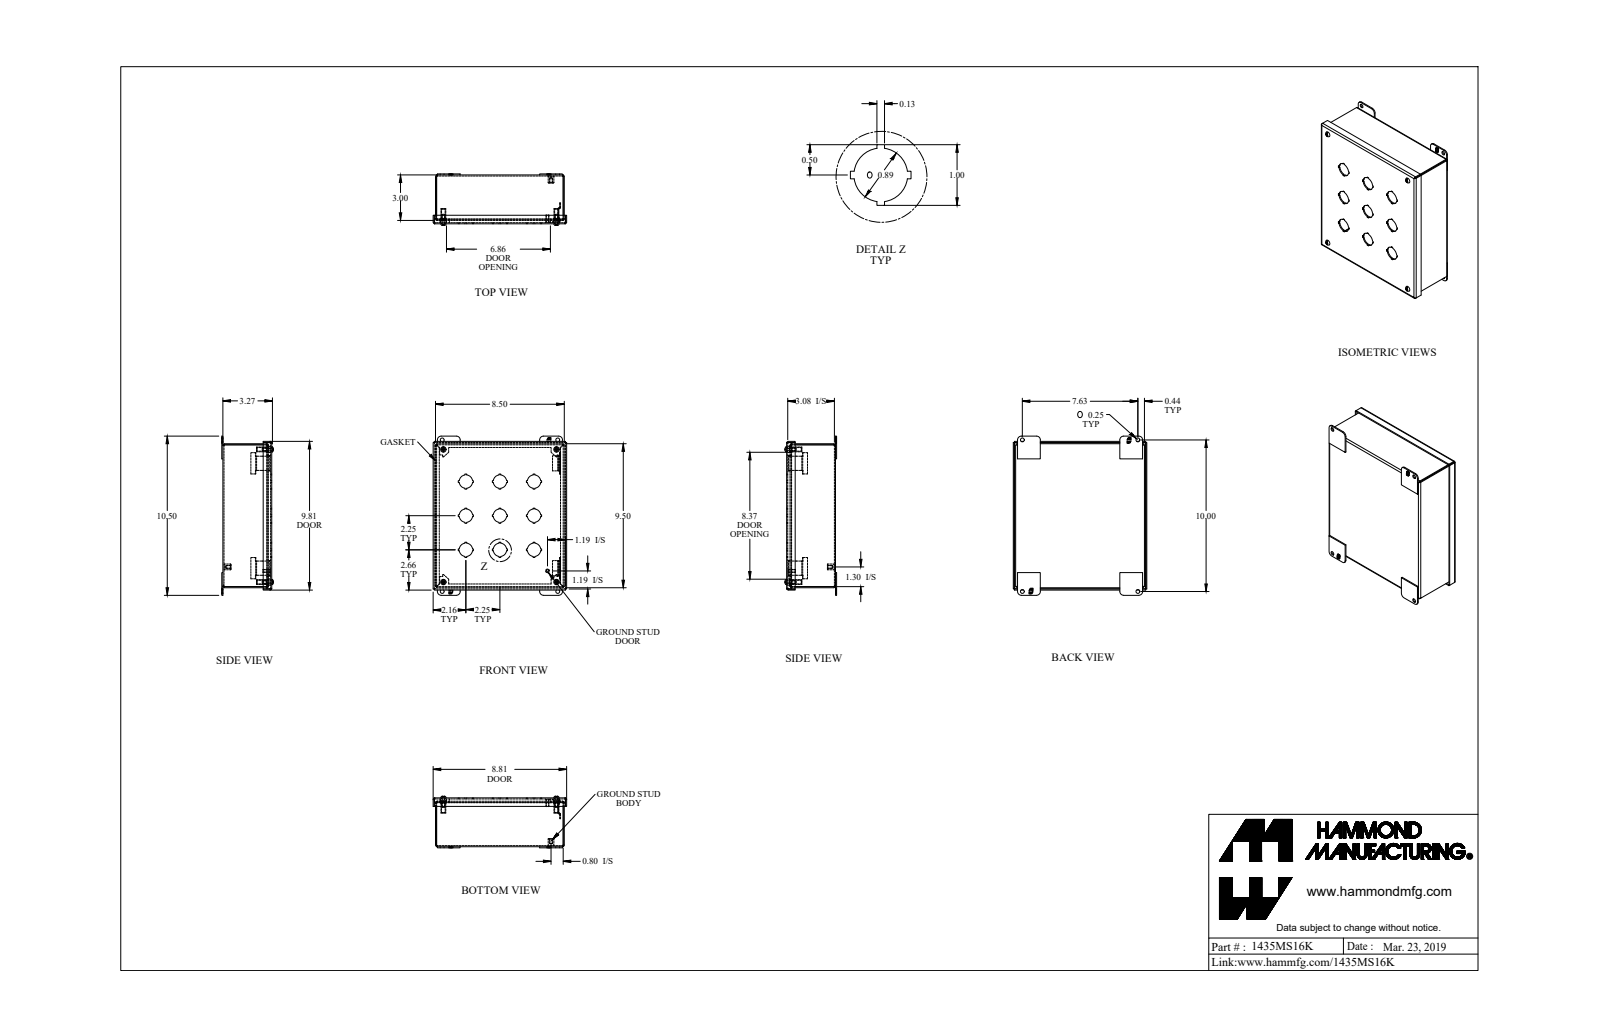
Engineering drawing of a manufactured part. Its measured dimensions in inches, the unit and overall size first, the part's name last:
Units: inches
Overall size (bounding box): 10.5 × 8.81 × 3.404
Round holes (diameter × count): ⌀0.886 ×9, ⌀0.25 ×8, ⌀0.065 ×4, ⌀0.239 ×4, ⌀0.253 ×4, ⌀0.406 ×4, ⌀0.156 ×1
Round bosses / shafts (diameter × count): ⌀0.19 ×5, ⌀0.406 ×4, ⌀0.315 ×4, ⌀0.148 ×4, ⌀0.375 ×1, ⌀0.25 ×1
Partial cylindrical surfaces — rounded edges, fillets, slot ends (radius × count): R0.036 ×12, R0.108 ×12, R0.25 ×8, R0.029 ×4, R0.086 ×4, R0.171 ×4
Main face-to-face distances: 0.072, 3.15, 3.222, 3.078, 8.428, 9.428, 0.155, 8.5, 8.356, 9.5
Hole centre spacings: 2.25, 3.182, 5.031, 7.46, 7.461, 7.569, 0.63, 4.5
Volume: 25.17 in³ · Surface area: 668.1 in²
Bodies: 23 solids, 749 faces (531 planar, 188 cylindrical, 30 other)
Part name (STEP PRODUCT): 1435MS16K_Default
STEP written by: SolidWorks 2019 (CONFIG_CONTROL_DESIGN)
